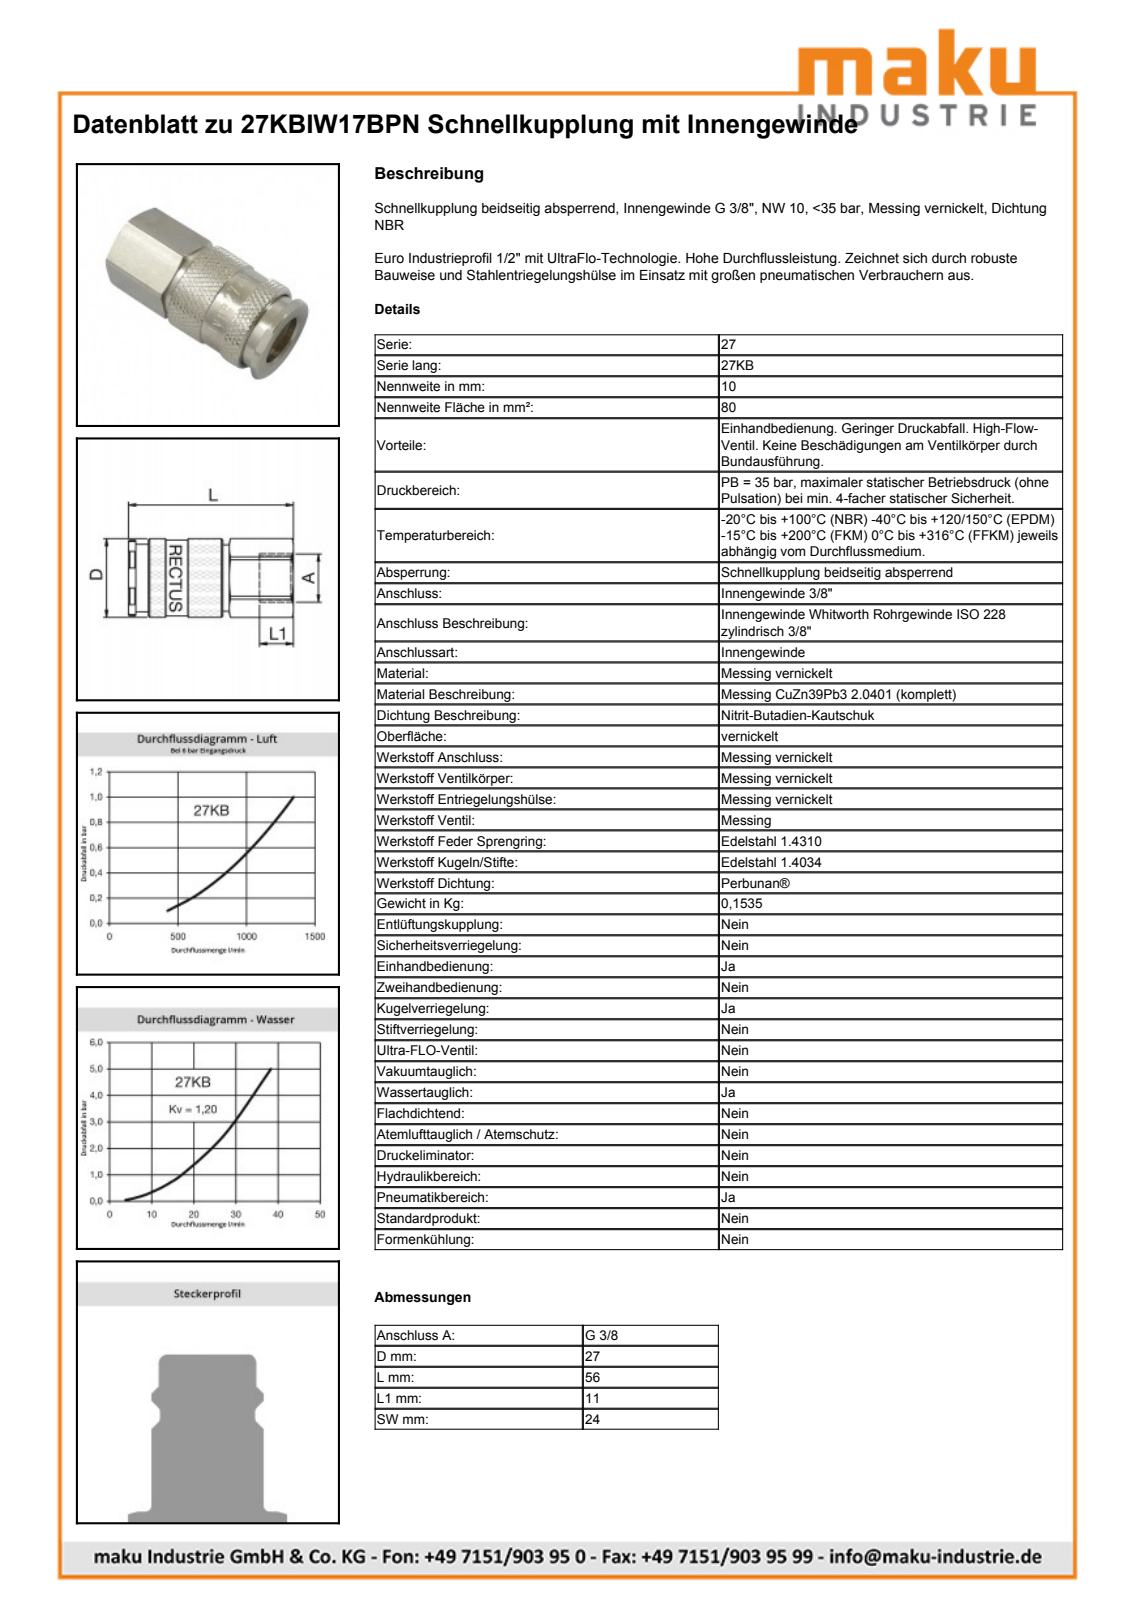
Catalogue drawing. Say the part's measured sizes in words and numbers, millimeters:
The part is named "D112126". Its 3-D file was written by "Autodesk Inventor 2013 (AUTOMOTIVE_DESIGN)". It is 2 solids with 707 faces: 228 planar, 85 cylindrical and 394 other. Overall it measures 56.45 by 27.15 by 27.15 millimeters. Its volume is 25 334 cubic millimeters and its surface area 11 151 square millimeters. Round holes: 1 of diameter 14.95, 1 of diameter 19, 1 of diameter 20.3, 1 of diameter 20.95, 1 of diameter 23.35, 1 of diameter 23.55. Round bosses or shafts: 1 of diameter 27.15, 1 of diameter 26, 1 of diameter 23.1, 1 of diameter 22.75, 1 of diameter 20, 1 of diameter 18.8, 1 of diameter 18.7, 1 of diameter 18.18. Partial cylindrical surfaces (rounded edges, fillets, slot ends): 1 of radius 9.9, 1 of radius 12.9, 1 of radius 13.53. The main face-to-face distances are 24, 24.02, 56.45, 45.73, 10.72, 31.9, 13.83, 24.55, 6.3, 25.6.
